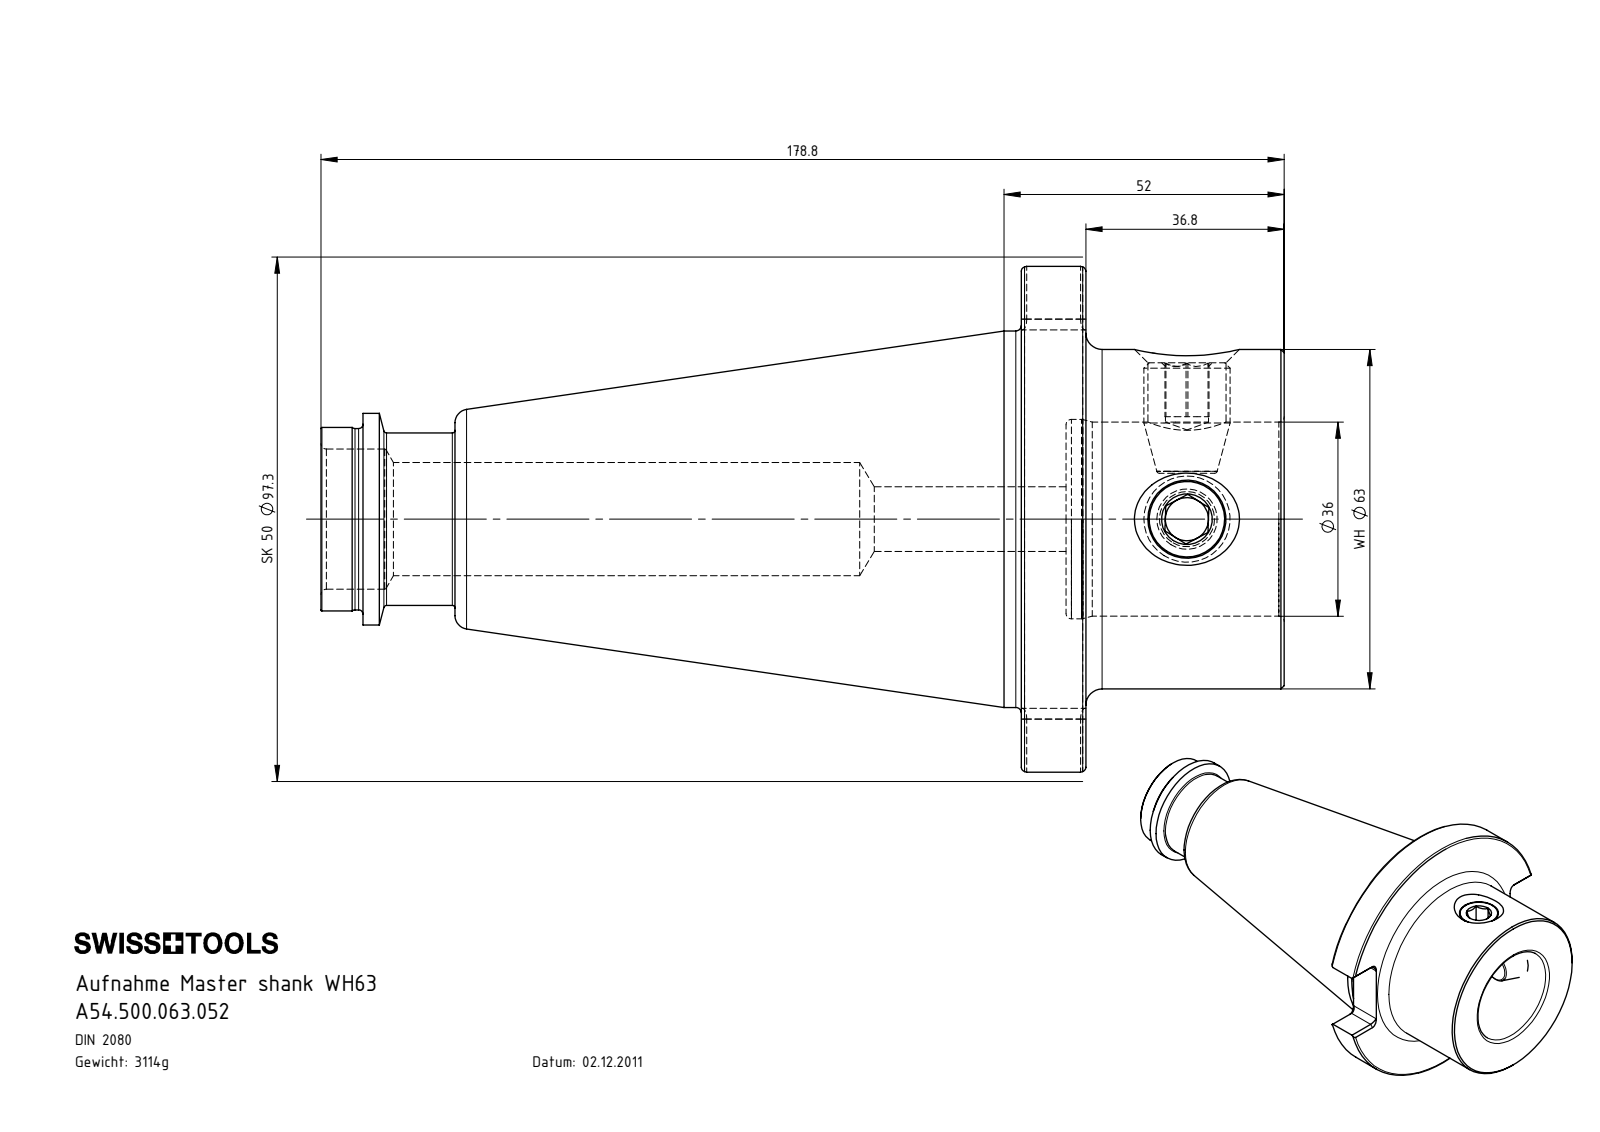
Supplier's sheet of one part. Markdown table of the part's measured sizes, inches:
| quantity | value |
| --- | --- |
| part name | SZ5-WH6.K01.052_B; WH6-ER1.001.021; A54.500.063.052 |
| STEP written by | SolidWorks 2022 (CONFIG_CONTROL_DESIGN) |
| units | inches |
| bodies | 3 solids, 166 faces (52 planar, 48 cylindrical, 66 other) |
| overall size | 7.039 × 3.831 × 3.694 |
| volume | 24.21 in³ |
| surface area | 92.23 in² |
| round holes (diameter × count) | 0.315 × 2, 0.571 × 2, 0.472 × 1, 0.827 × 1, 1.024 × 1, 1.417 × 1, 1.457 × 1 |
| round bosses / shafts (diameter × count) | 0.63 × 2, 3.831 × 1, 2.75 × 1, 2.48 × 1, 1.545 × 1, 1.341 × 1, 1.325 × 1, 1.26 × 1 |
| partial cylindrical surfaces (radius × count) | 0.079 × 12 |
| main face-to-face distances | 0.472, 1.921, 1.449, 0.327, 0.146, 1.594, 5.118, 5.445, 5.591, 7.039 |
